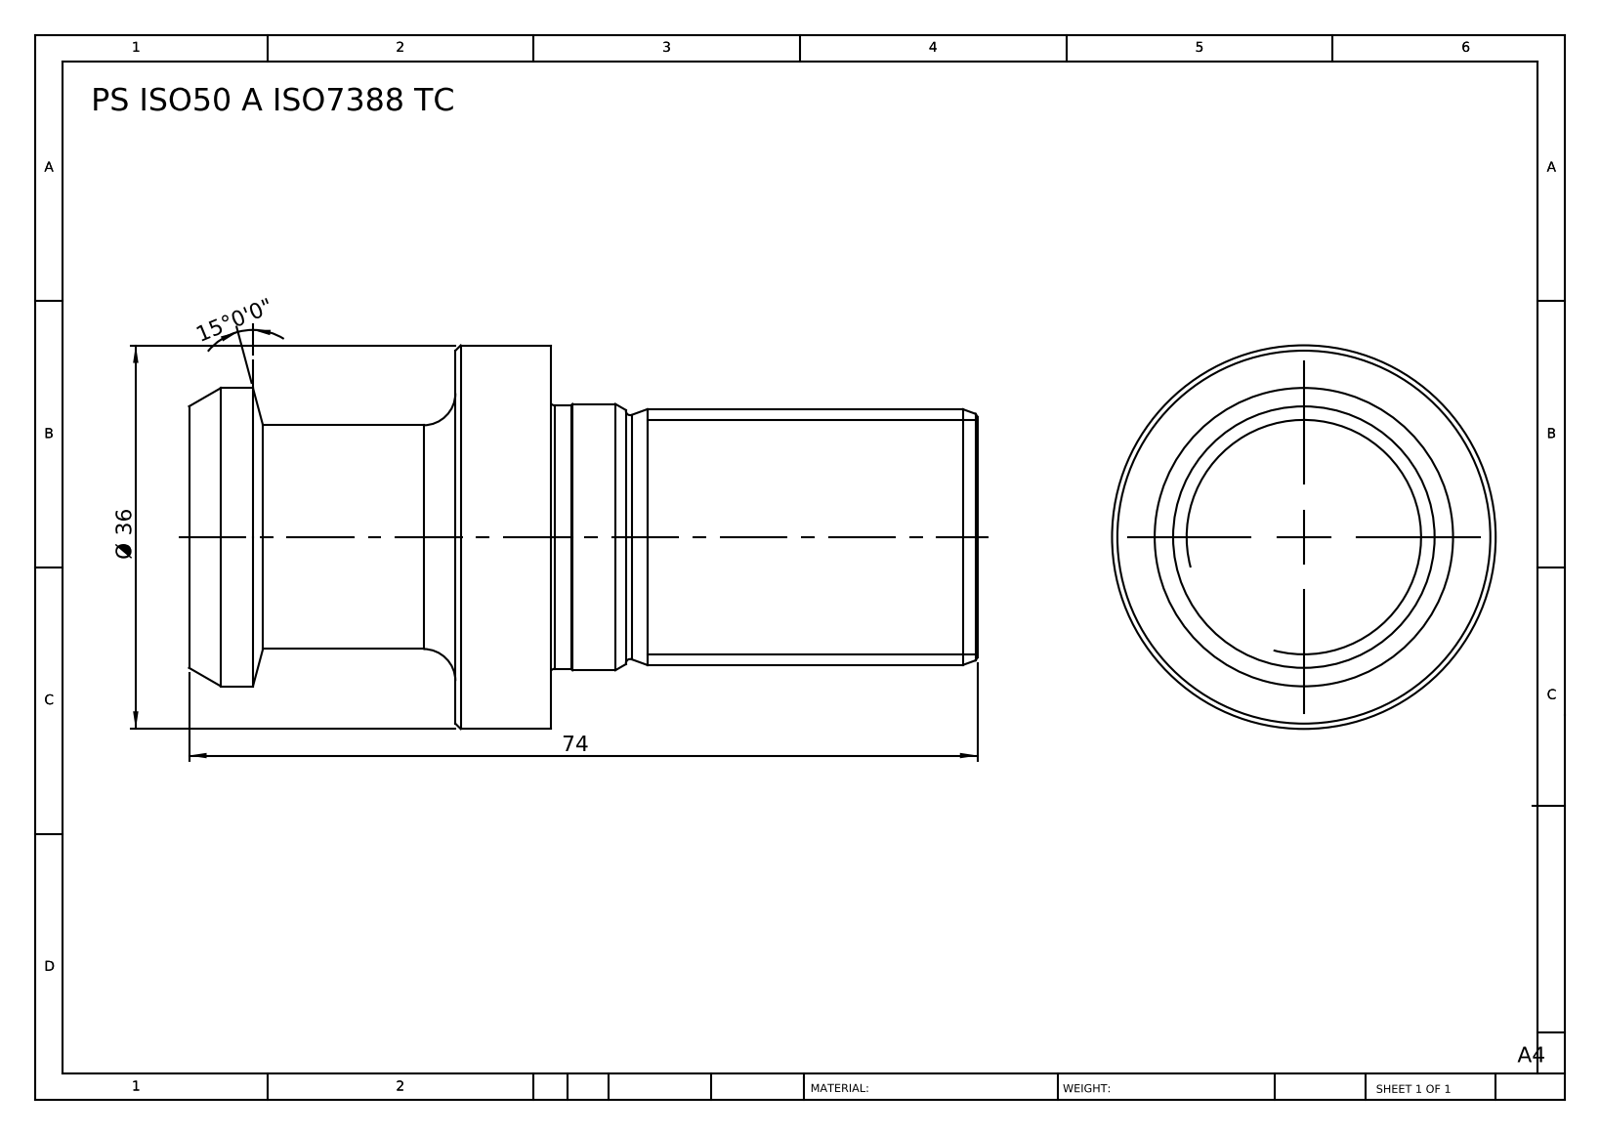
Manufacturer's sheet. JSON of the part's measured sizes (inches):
{"part_name": "PS ISO50 A ISO7388 TC", "step_written_by": "SolidWorks 2014 (CONFIG_CONTROL_DESIGN)", "units": "inches", "bodies": {"solids": 1, "faces": 43, "planar": 5, "cylindrical": 12, "other": 26}, "overall_size": [2.913, 1.417, 1.417], "volume_in3": 2.3, "surface_area_in2": 12.55, "round_bosses_or_shafts": [[1.417, 1], [1.102, 1], [0.984, 1], [0.972, 1], [0.945, 1], [0.827, 1]], "face_to_face_distances": [1.339, 1.575, 2.913, 1.929, 0.354, 0.984, 1.299, 0.276, 0.63, 1.614]}
